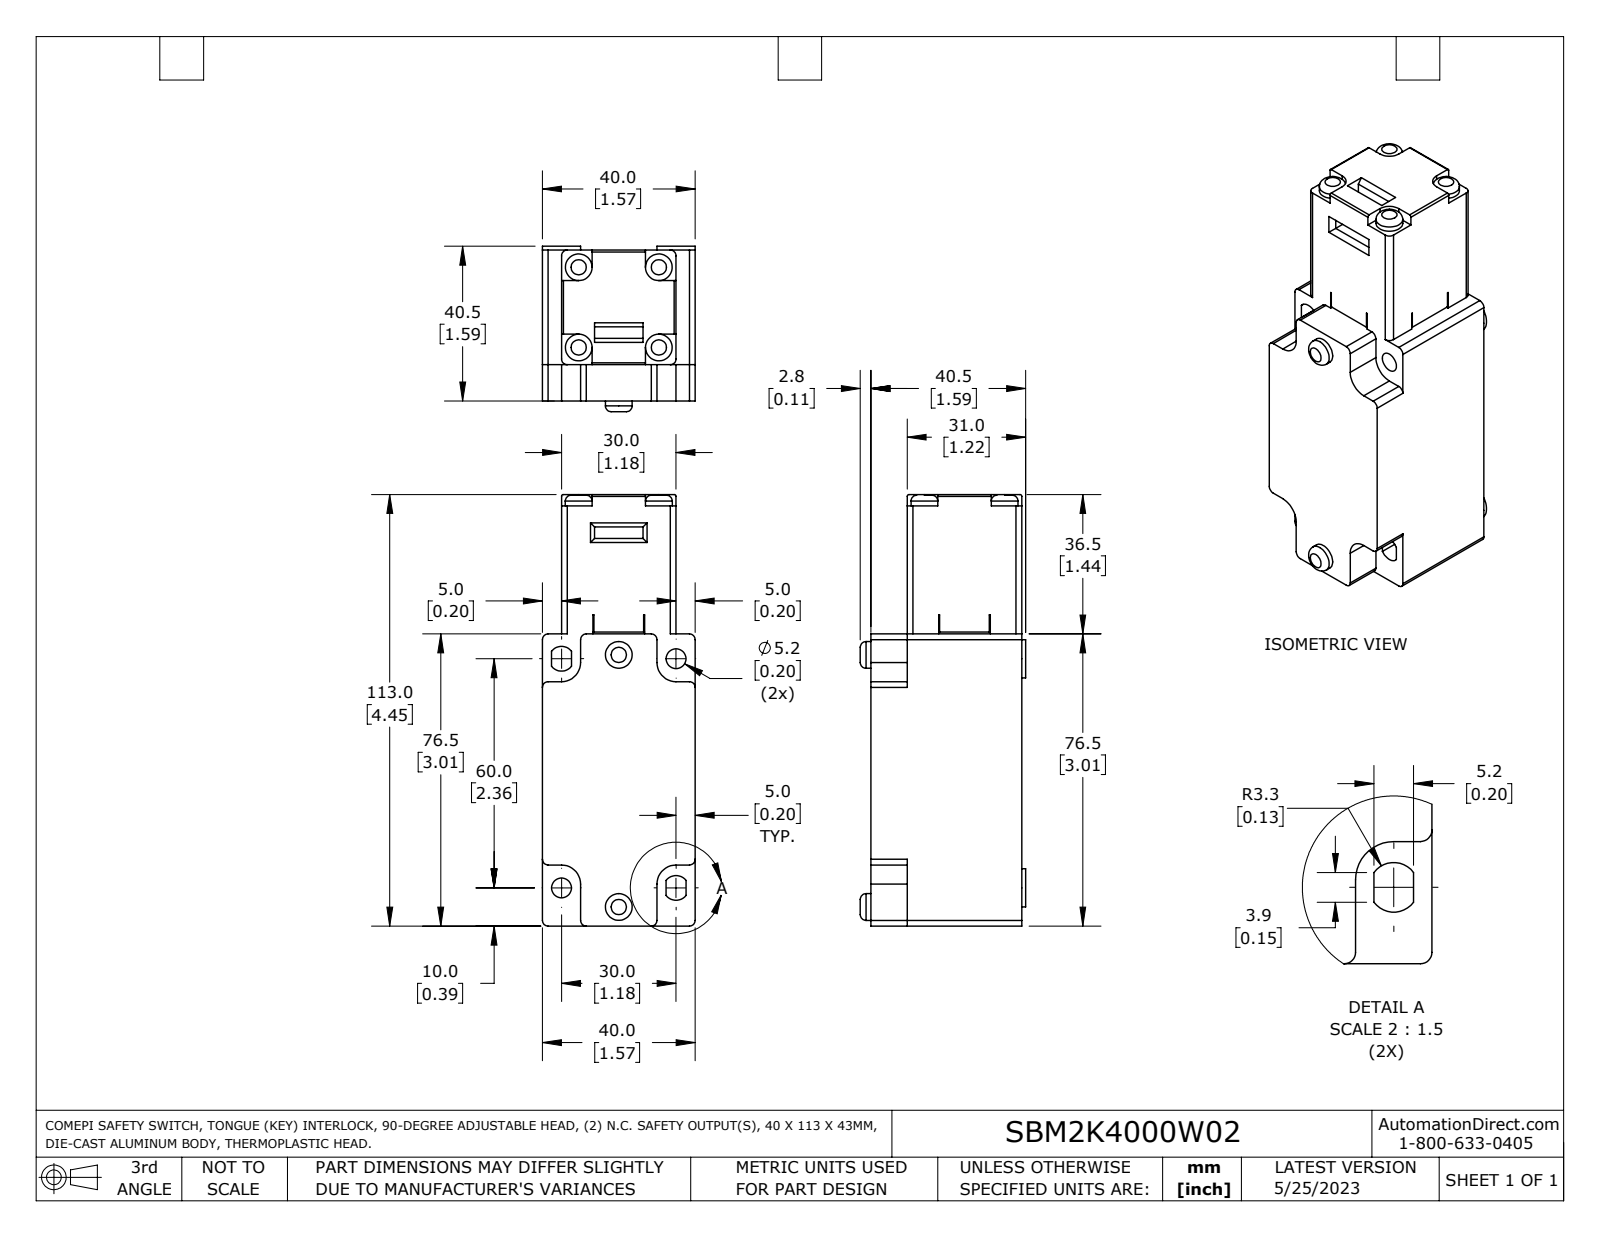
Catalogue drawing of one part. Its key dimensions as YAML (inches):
part_name: "SBM2K4000W02"
step_written_by: "SolidWorks 2021 (AUTOMOTIVE_DESIGN)"
units: inches
bodies: {solids: 1, faces: 147, planar: 86, cylindrical: 54, other: 7}
overall_size: [4.449, 1.705, 1.575]
volume: 8.506
surface_area: 40.19
round_holes:
  - {diameter: 0.276, count: 4}
  - {diameter: 0.205, count: 2}
  - {diameter: 0.669, count: 1}
  - {diameter: 0.748, count: 1}
round_bosses_or_shafts:
  - {diameter: 0.394, count: 4}
  - {diameter: 0.276, count: 2}
partial_cylinders:
  - {radius: 0.059, count: 16}
  - {radius: 0.02, count: 4}
  - {radius: 0.197, count: 4}
  - {radius: 0.128, count: 2}
  - {radius: 0.453, count: 1}
  - {radius: 0.472, count: 1}
face_to_face_distances: [1.181, 1.575, 1.555, 0.197, 1.378, 0.374, 3.012, 0.118, 0.02, 0.984]
hole_center_spacings: [0.827, 0.557, 0.613, 1.169, 2.641]
